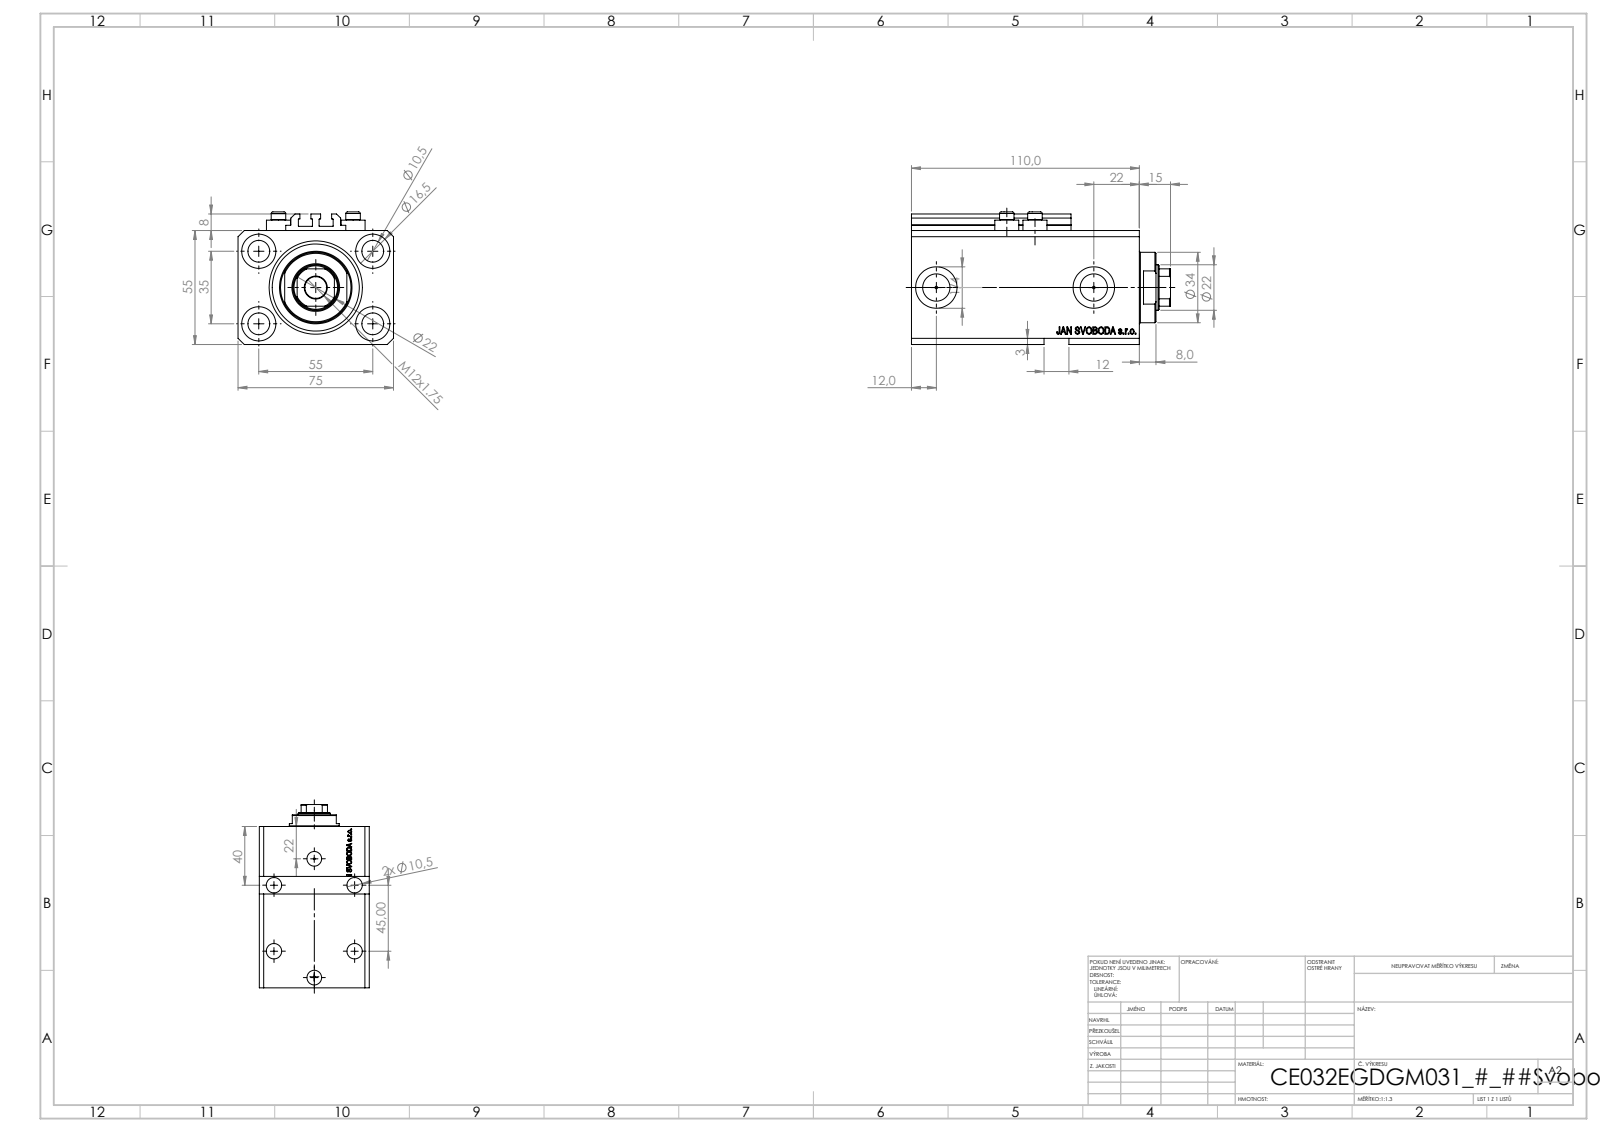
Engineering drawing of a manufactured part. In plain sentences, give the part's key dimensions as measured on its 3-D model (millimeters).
The part is named "ALLEN BOLT V250CE; V250CE_E_Body; V250CE_VC_E; V250CE_C_VCP". Its 3-D file was written by "SolidWorks 2019 (CONFIG_CONTROL_DESIGN)". It is 8 solids with 1100 faces: 518 planar, 158 cylindrical and 424 other. Overall it measures 125 by 75 by 64 millimeters. Its volume is 377 718 cubic millimeters and its surface area 96 791 square millimeters. Round holes: 9 of diameter 10.5, 4 of diameter 1.25, 4 of diameter 4, 4 of diameter 16.5, 2 of diameter 10, 2 of diameter 13.16, 2 of diameter 20, 1 of diameter 22, 1 of diameter 32, 1 of diameter 45. Round bosses or shafts: 4 of diameter 11.6, 4 of diameter 7, 1 of diameter 34. Partial cylindrical surfaces (rounded edges, fillets, slot ends): 10 of radius 0.2, 1 of radius 10.5. The main face-to-face distances are 55, 75, 15, 110, 95, 9.9, 3, 85.1, 100.1, 57. The hole center spacings are 32.6, 32.87, 55, 68.74, 13.6, 14.09, 23.05, 25.81.
